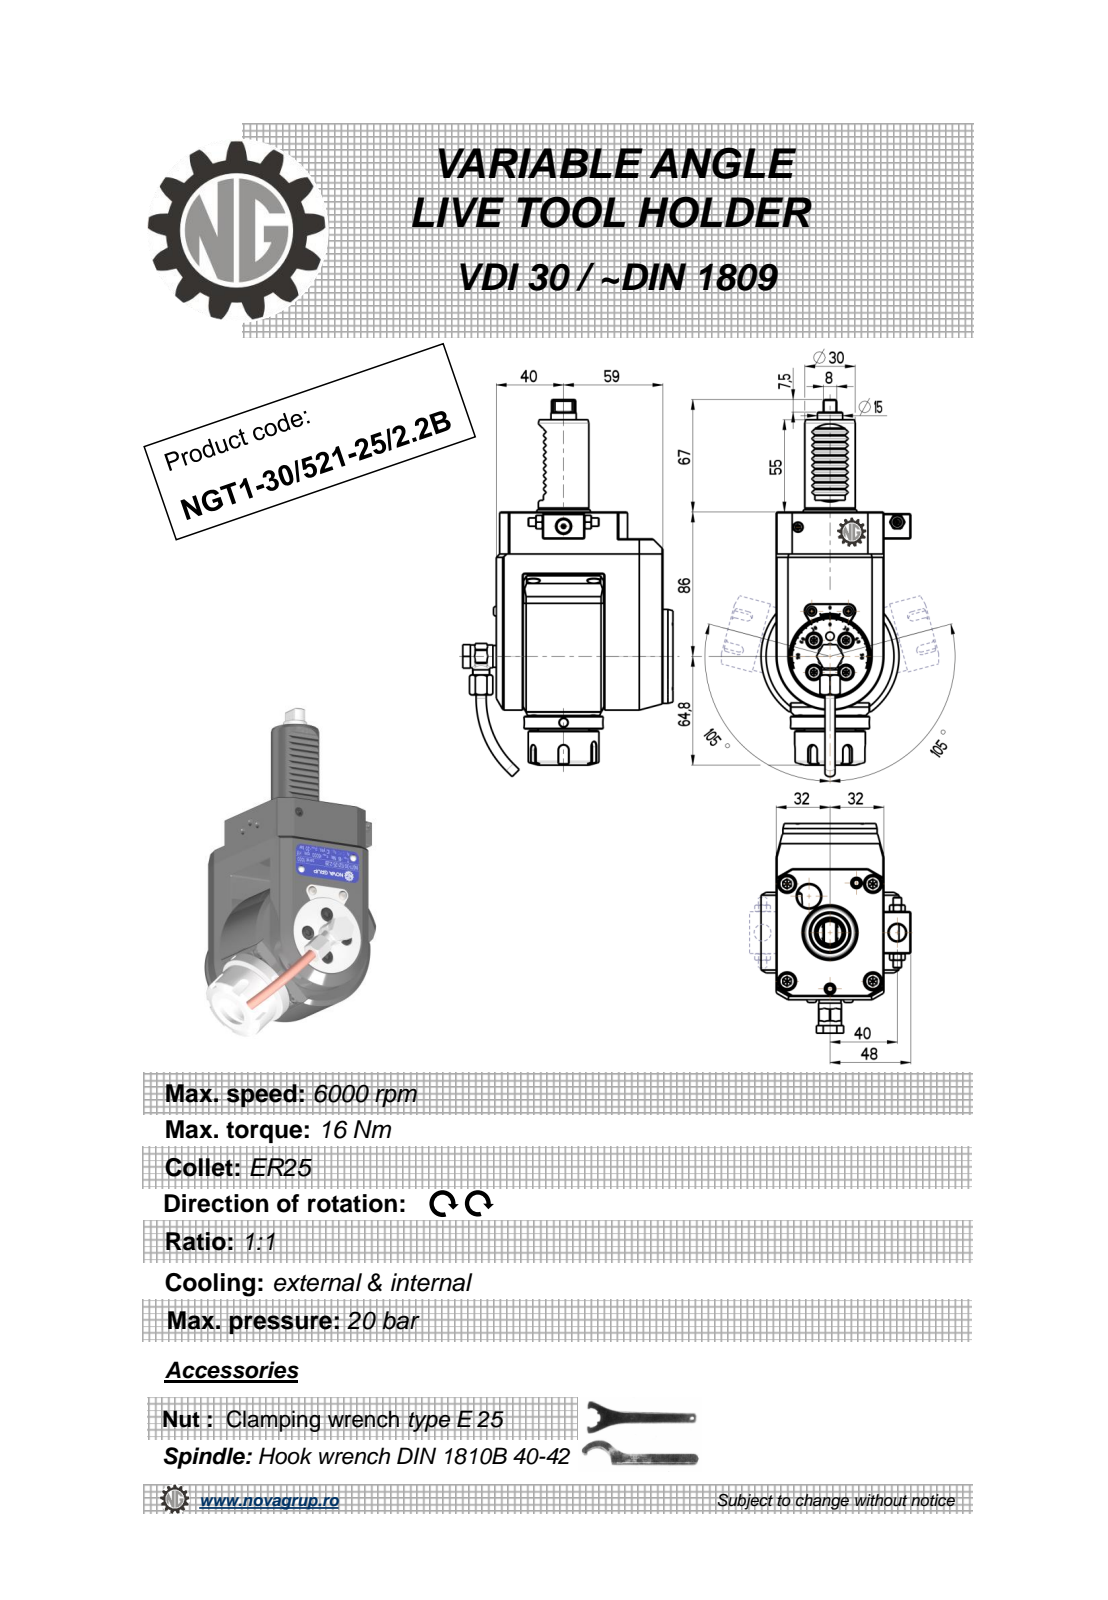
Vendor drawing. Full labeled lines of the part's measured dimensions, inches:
Part name (STEP PRODUCT): NGT1_30_521_25_2_2B
STEP written by: PRO/ENGINEER BY PARAMETRIC TECHNOLOGY CORPORATION, 2010280 (CONFIG_CONTROL_DESIGN)
Units: inches
Bodies: 1 solid, 573 faces (245 planar, 140 cylindrical, 188 other)
Overall size (bounding box): 8.845 × 4.917 × 3.504
Volume: 48.99 in³ · Surface area: 116.8 in²
Round holes (diameter × count): ⌀0.157 ×3, ⌀0.197 ×2, ⌀0.118 ×1, ⌀0.165 ×1, ⌀0.244 ×1, ⌀0.354 ×1, ⌀0.374 ×1, ⌀0.394 ×1, ⌀0.433 ×1, ⌀0.799 ×1
Round bosses / shafts (diameter × count): ⌀0.394 ×2, ⌀0.236 ×2, ⌀0.224 ×2, ⌀2.205 ×1, ⌀1.85 ×1, ⌀1.654 ×1, ⌀1.378 ×1, ⌀1.181 ×1
Partial cylindrical surfaces — rounded edges, fillets, slot ends (radius × count): R0.01 ×12, R0.012 ×10, R0.006 ×6, R0.118 ×5, R0.02 ×4, R0.031 ×2, R0.039 ×2, R0.283 ×1
Main face-to-face distances: 2.52, 0.63, 1.457, 0.236, 3.898, 4.134, 0.551, 0.827, 2.441, 1.378
Hole centre spacings: 0.016, 1.553, 1.575, 1.929, 1.945, 2.49, 2.502, 3.521
